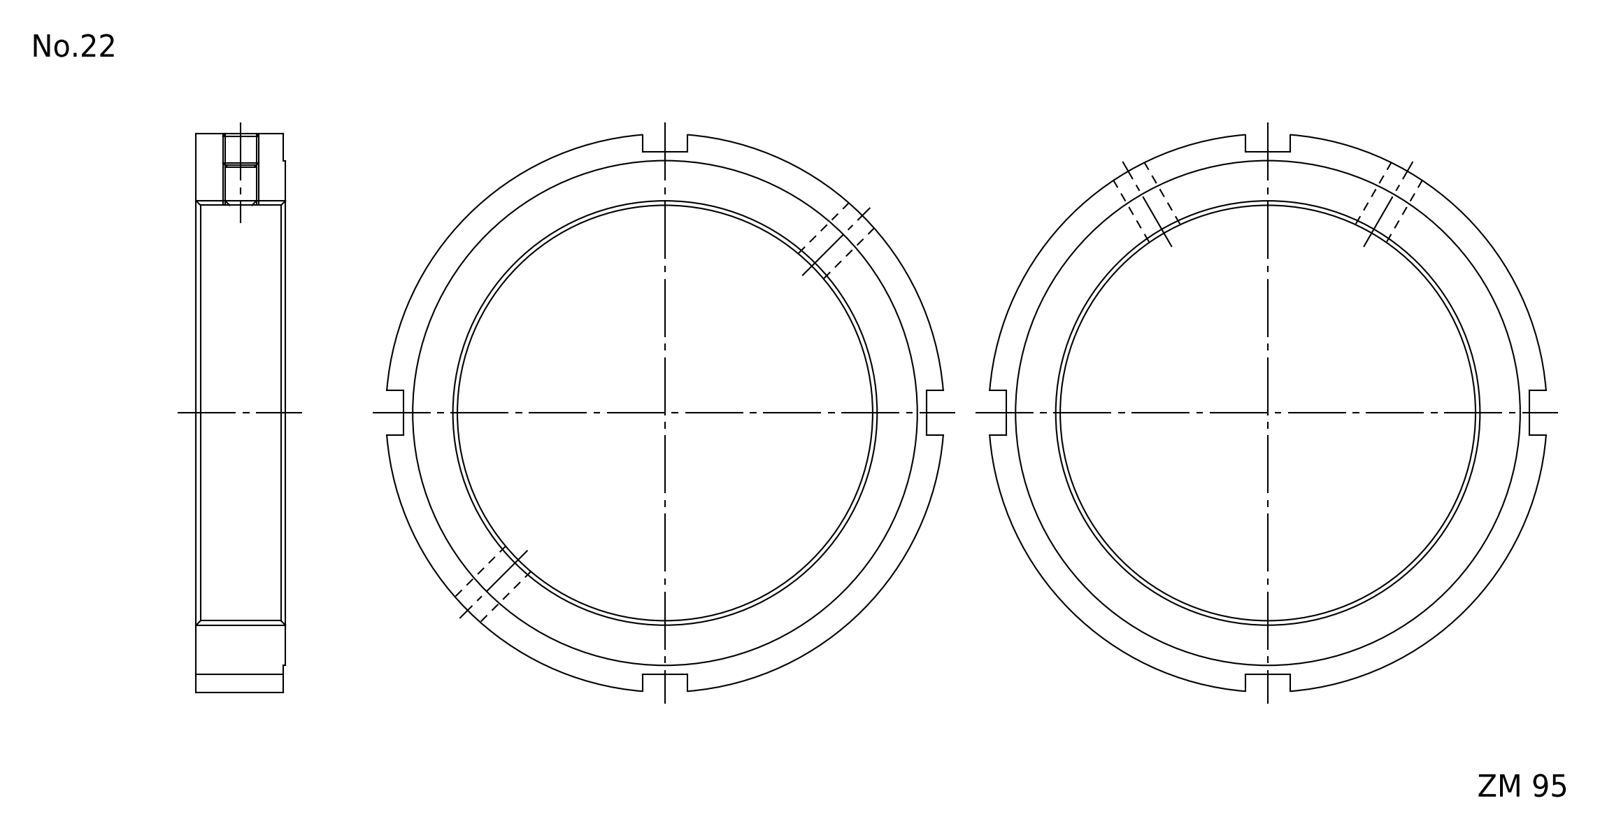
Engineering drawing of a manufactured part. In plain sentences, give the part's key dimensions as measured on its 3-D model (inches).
The part is named "FKD ZM 95". Its 3-D file was written by "Autodesk Inventor 2011 (AUTOMOTIVE_DESIGN)". It is 1 solid with 23 faces: 15 planar, 8 cylindrical and 0 other. Overall it measures 4.906 by 4.906 by 0.787 inches. Its volume is 6.007 cubic inches and its surface area 38.65 square inches. Round holes: 2 of diameter 0.262, 1 of diameter 3.74. Round bosses or shafts: 1 of diameter 4.921, 1 of diameter 4.449. The main face-to-face distances are 0.787, 0.02, 0.768, 2.106, 2.5, 4.606, 0.394.
